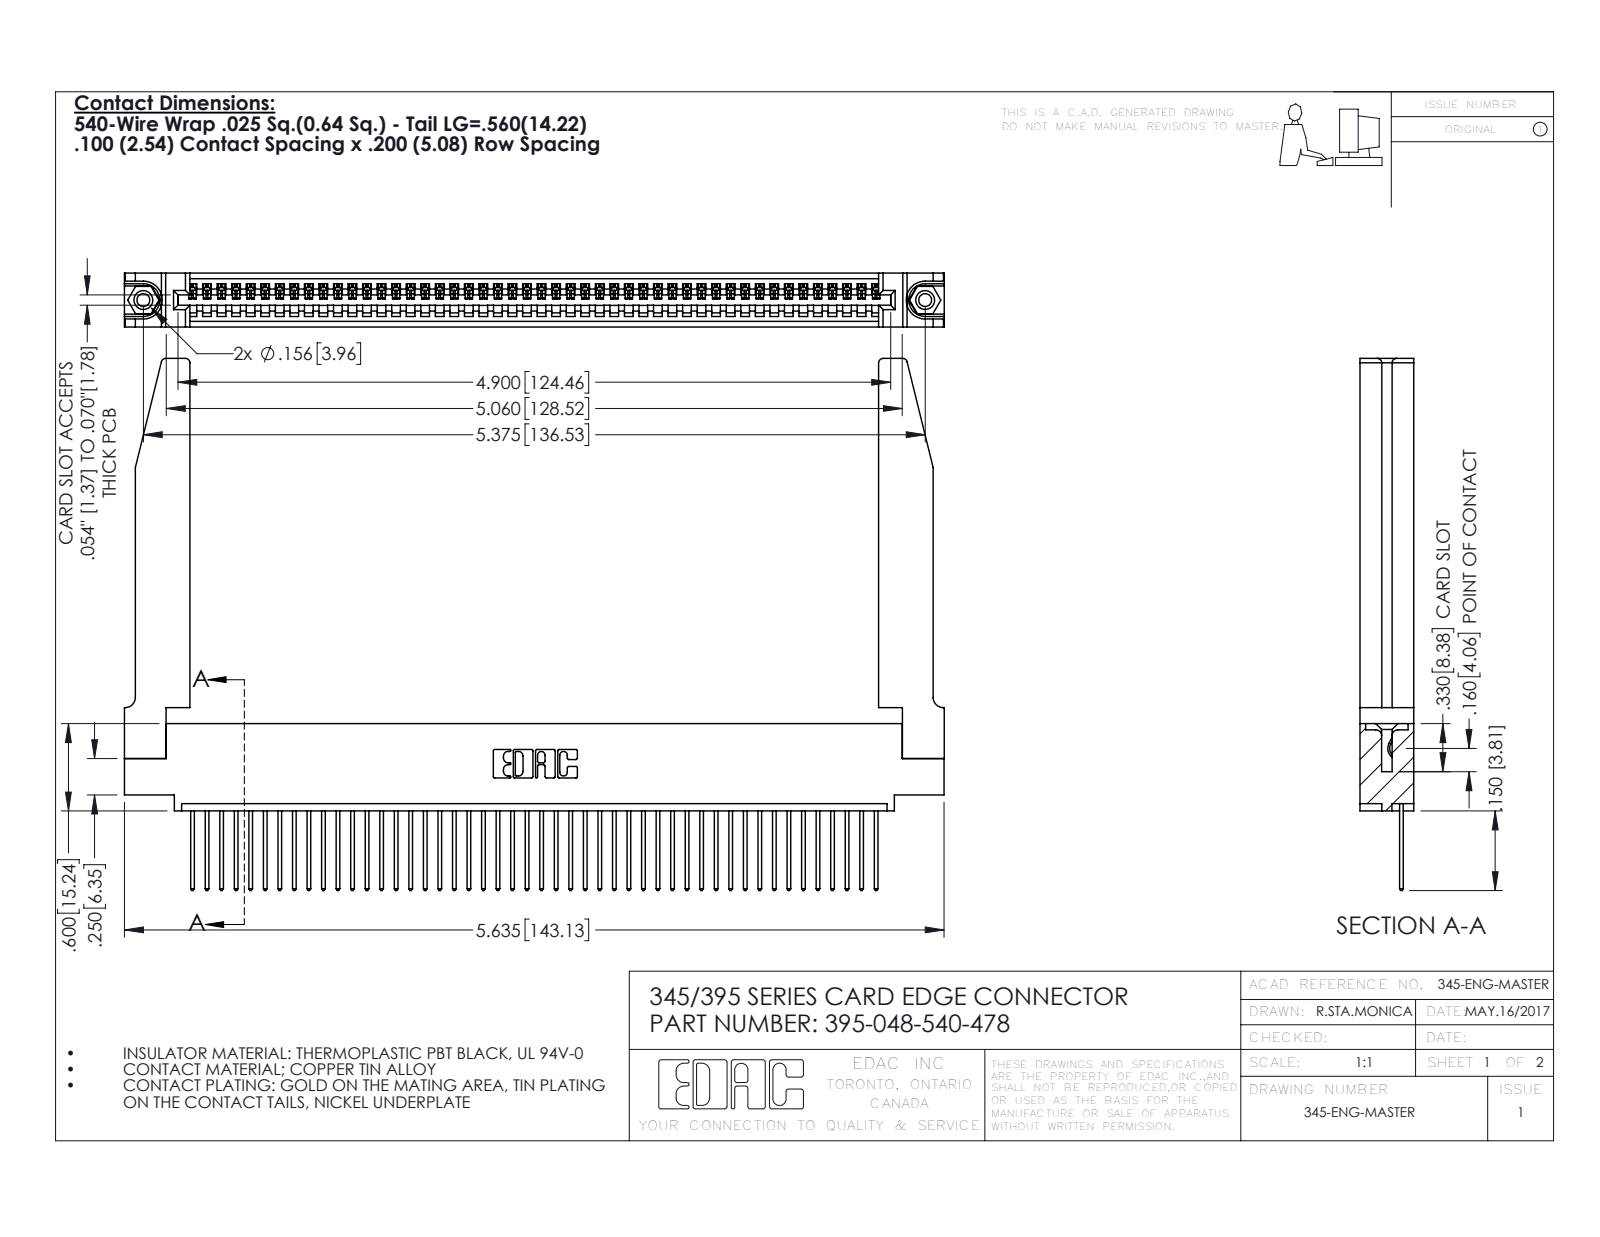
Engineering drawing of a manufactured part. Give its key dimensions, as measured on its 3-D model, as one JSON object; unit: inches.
{"part_name": "345-292-001_345-293-140; 345 Part_0.110 Offset - 0.156 Dia-TH; 345-220-078_345-220-078; 395-048-540-478 (+1 more)", "step_written_by": "SolidWorks 2016 (CONFIG_CONTROL_DESIGN)", "units": "inches", "bodies": {"solids": 53, "faces": 3148, "planar": 2146, "cylindrical": 950, "other": 52}, "overall_size": [5.636, 3.657, 0.37], "volume_in3": 1.306, "surface_area_in2": 39.68, "round_holes": [[0.089, 2], [0.125, 2], [0.156, 2], [0.064, 1]], "round_bosses_or_shafts": [[0.155, 2]], "partial_cylinders_radius": [[0.006, 96], [0.01, 96], [0.01, 22], [0.03, 8], [0.007, 6], [0.031, 6], [0.026, 3], [0.031, 2]], "face_to_face_distances": [0.072, 0.37, 0.298, 0.098, 0.272, 0.025, 0.2, 0.225, 0.15, 0.148], "hole_center_spacings": [0.27, 5.139, 5.375]}
